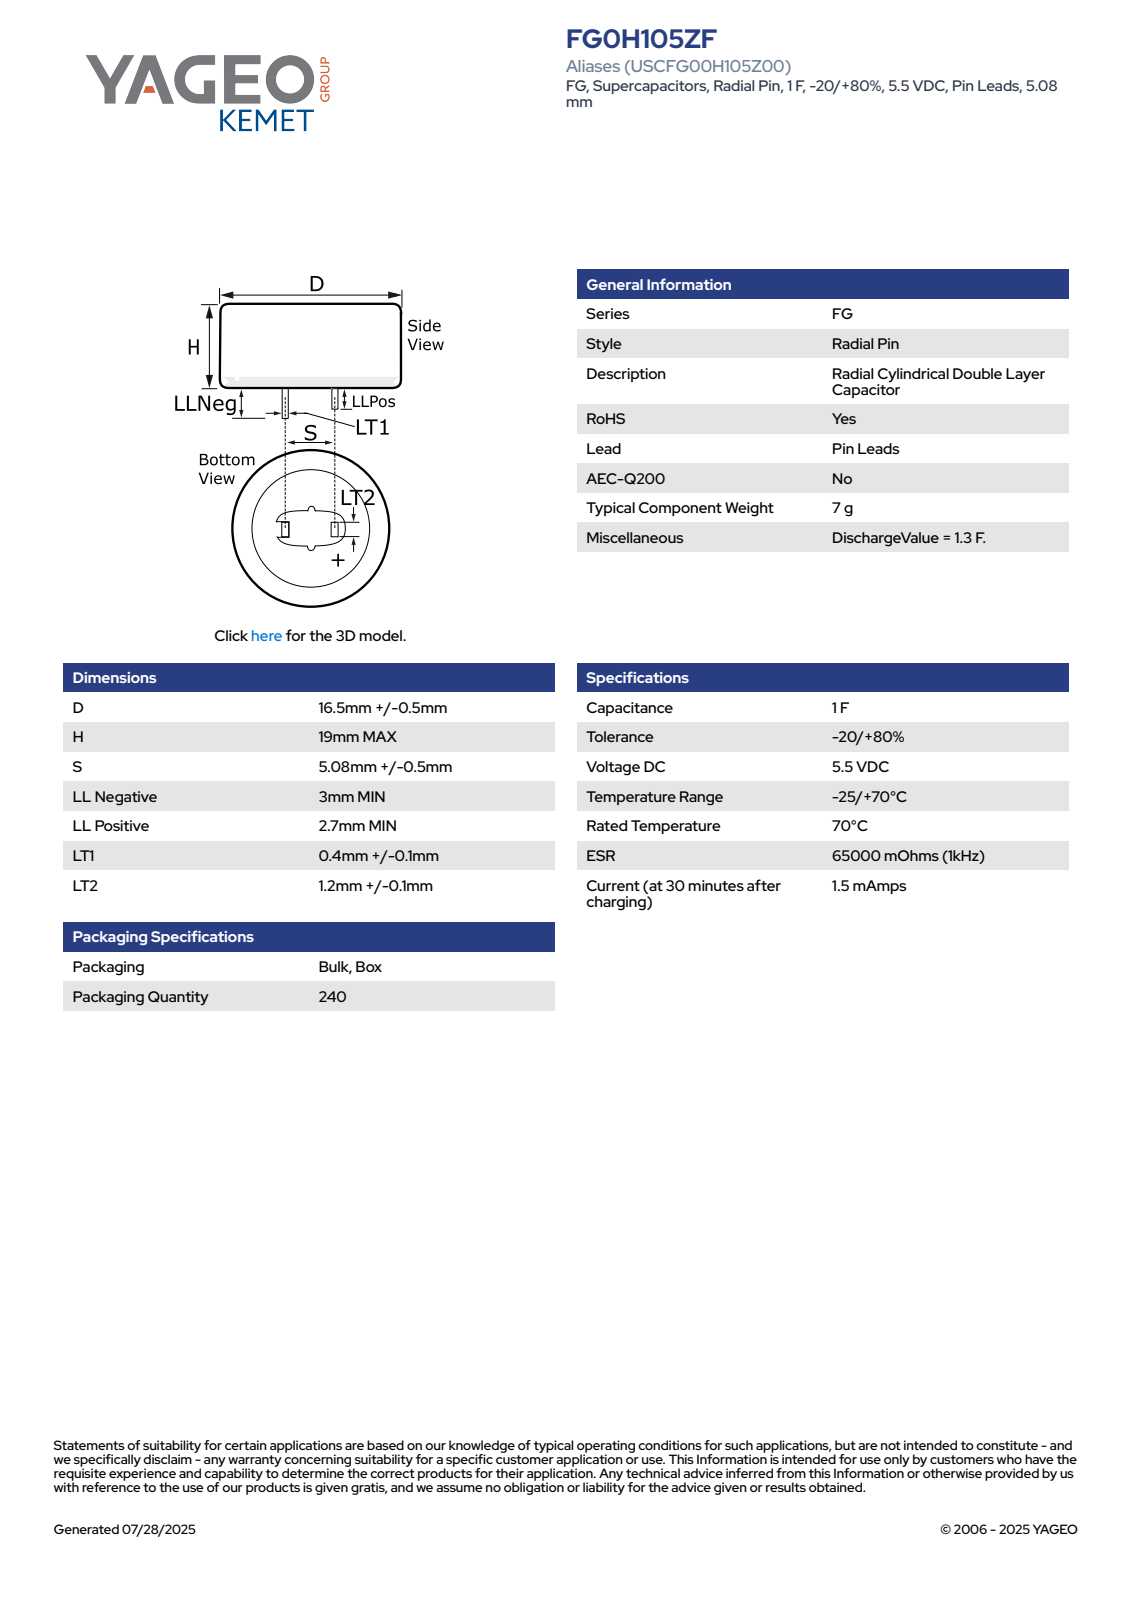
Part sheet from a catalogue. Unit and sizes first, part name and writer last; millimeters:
Units: millimetres
Overall size (bounding box): 22 × 17 × 17
Round bosses / shafts (diameter × count): ⌀17 ×1
Partial cylindrical surfaces — rounded edges, fillets, slot ends (radius × count): R8.51 ×1
Main face-to-face distances: 19, 18.99, 0.5, 5.08, 5.58, 4.58, 1.3, 3, 21.99, 22
Volume: 4 283 mm³ · Surface area: 1 432 mm²
Bodies: 1 solid, 78 faces (70 planar, 4 cylindrical, 4 other)
Part name (STEP PRODUCT): CDR_LPLLN_D17L19S5.08LLNEG3LLPOS2.7LT10.5LT21.3
STEP written by: SolidWorks 2014 (AUTOMOTIVE_DESIGN)
